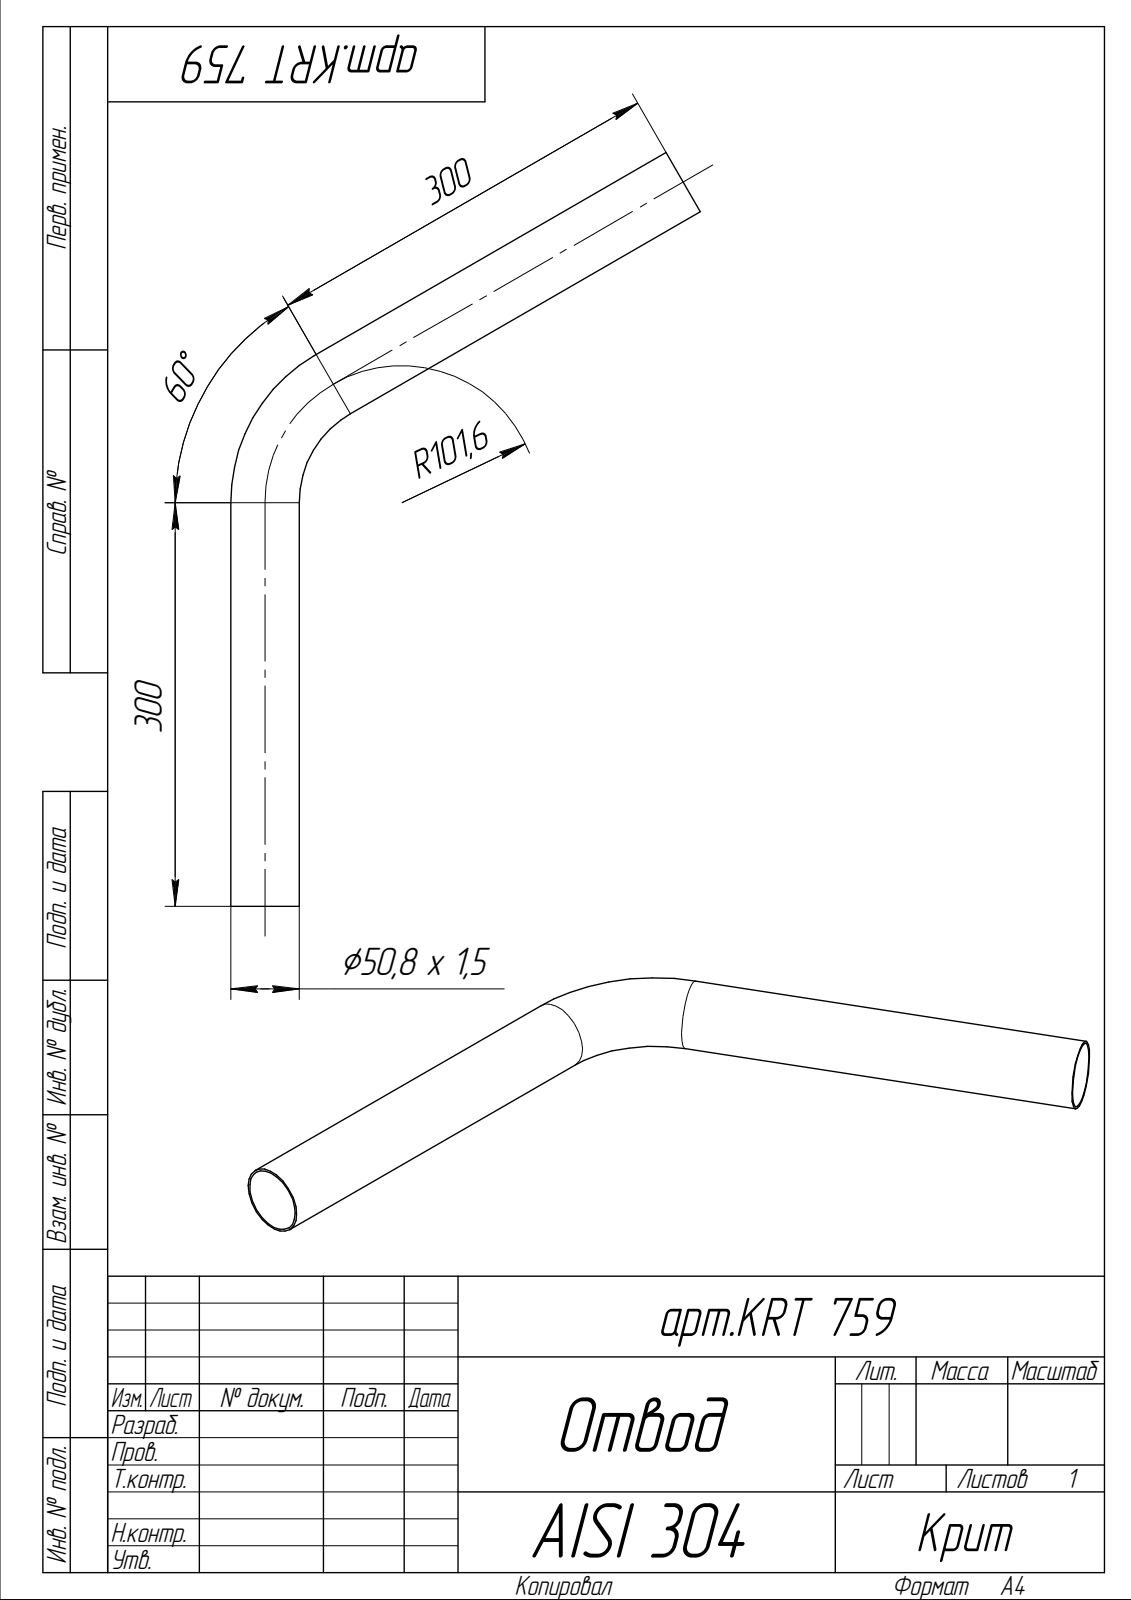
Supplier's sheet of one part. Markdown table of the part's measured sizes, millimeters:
| quantity | value |
| --- | --- |
| part name | Деталь |
| STEP written by | ASCON Math Kernel (AUTOMOTIVE_DESIGN) |
| units | millimeters |
| bodies | 1 solid, 8 faces (2 planar, 4 cylindrical, 2 other) |
| overall size | 559.99 × 348.71 × 50.8 |
| volume | 164 110 mm³ |
| surface area | 219 278 mm² |
| round holes (diameter × count) | 47.8 × 2 |
| round bosses / shafts (diameter × count) | 50.8 × 2 |
